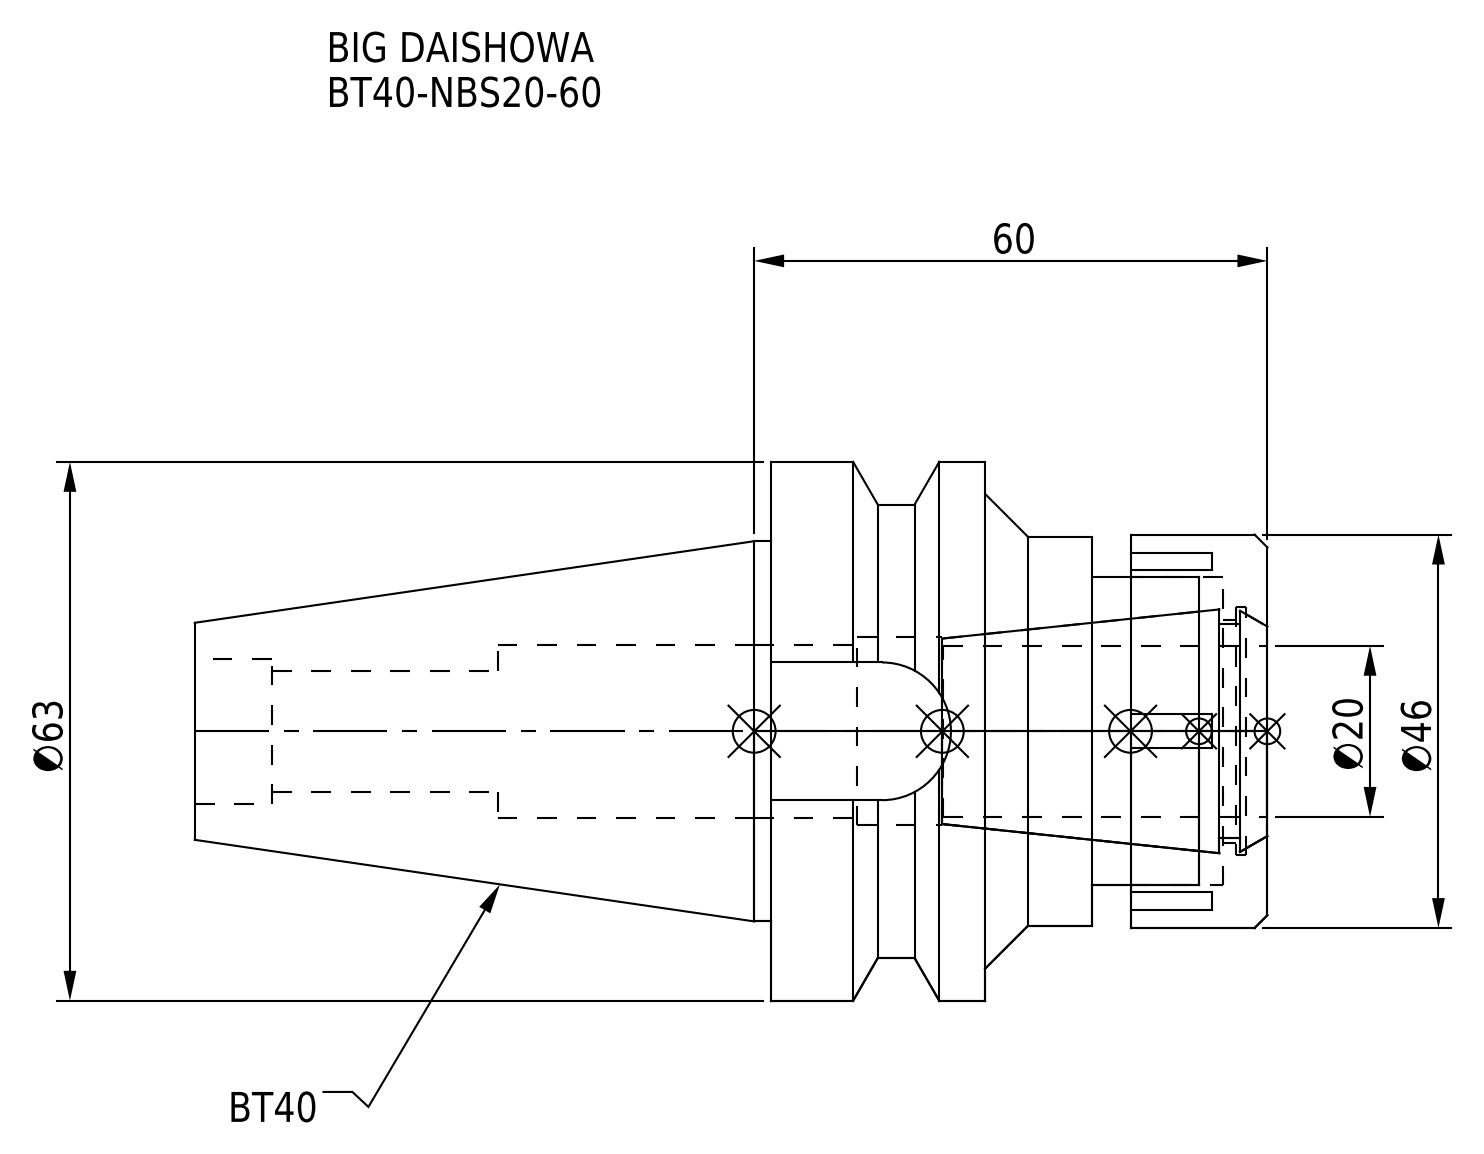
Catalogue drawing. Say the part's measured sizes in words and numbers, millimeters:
The part is named "NBN20_1.stp; BT40NB20060-200_ASM.stp; DXF_TEMP_ASSY_ASM_4_ASM.stp; BT40-NBS20-60_1.stp (+3 more)". Its 3-D file was written by "SolidWorks 2019 (CONFIG_CONTROL_DESIGN)". It is 2 solids with 90 faces: 44 planar, 32 cylindrical and 14 other. Overall it measures 125.4 by 63 by 63 millimeters. Its volume is 142 864 cubic millimeters and its surface area 35 103 square millimeters. Round holes: 1 of diameter 14.2, 1 of diameter 17, 1 of diameter 20.3, 1 of diameter 22, 1 of diameter 26, 1 of diameter 29, 1 of diameter 36. Round bosses or shafts: 1 of diameter 63, 1 of diameter 53, 1 of diameter 46, 1 of diameter 45.5, 1 of diameter 44.45. Partial cylindrical surfaces (rounded edges, fillets, slot ends): 1 of radius 8.05. The main face-to-face distances are 25, 12.5, 58, 8, 33, 42, 20.5, 37.5, 16, 4.5.
